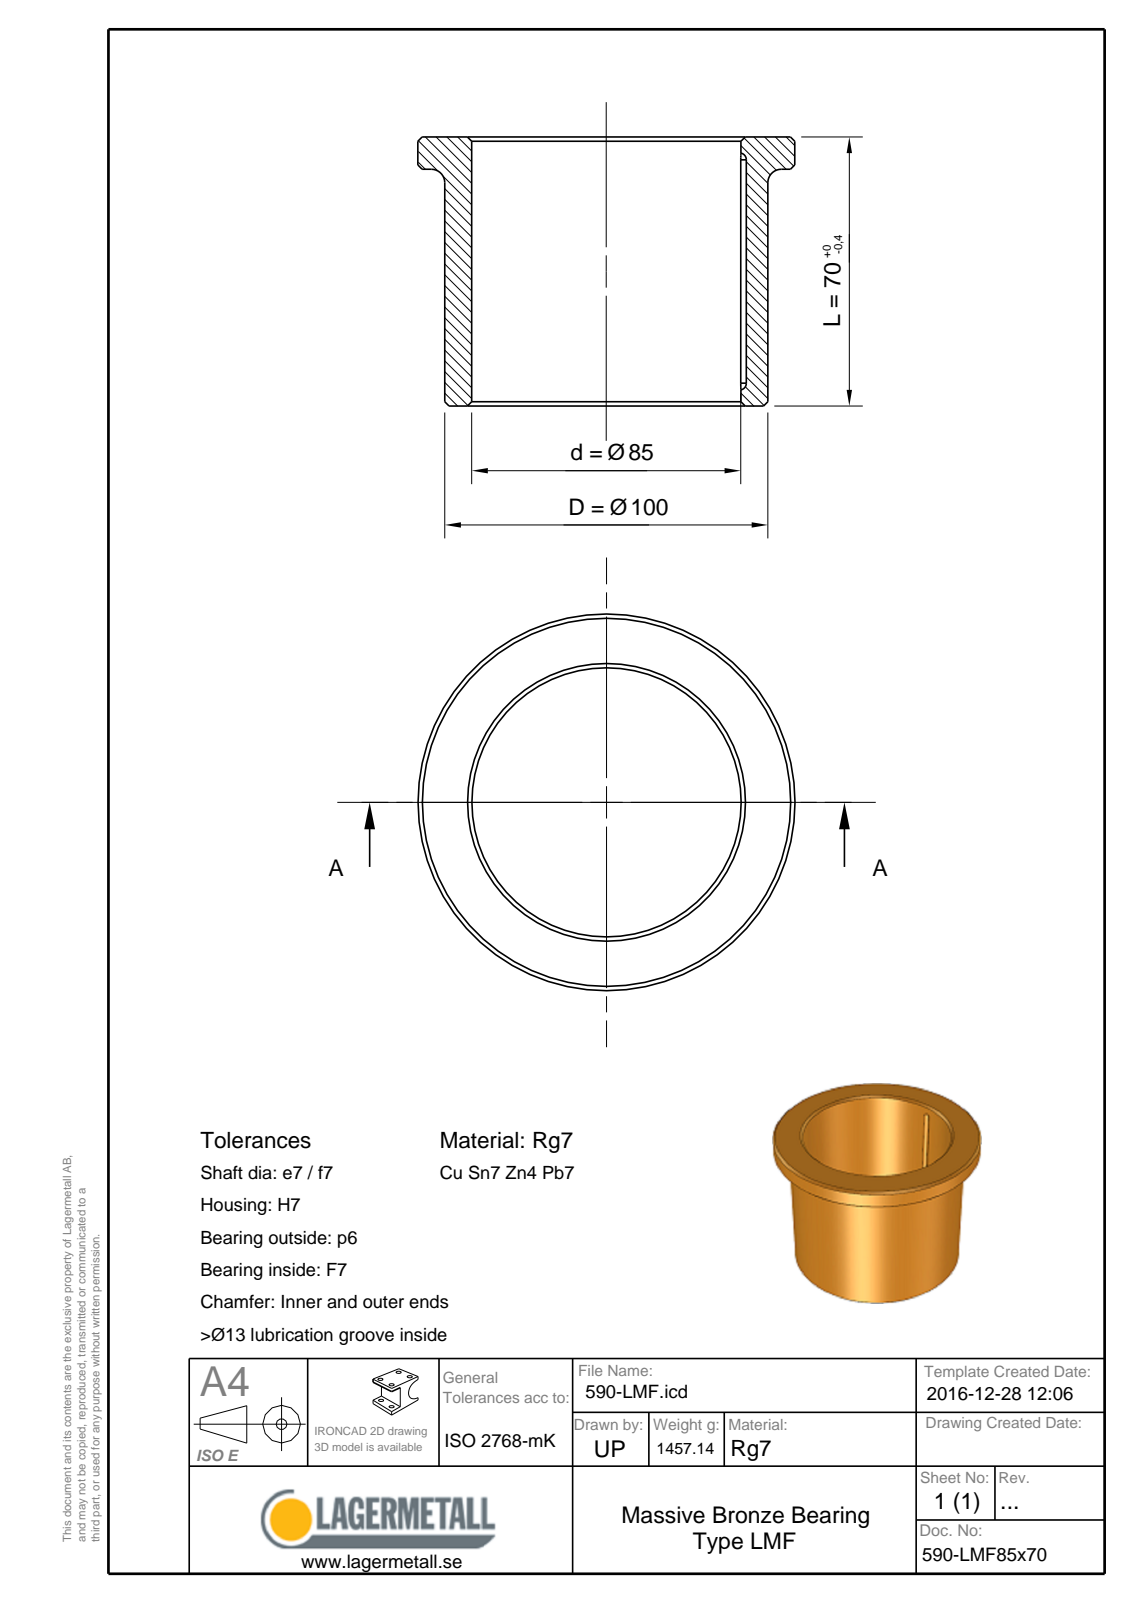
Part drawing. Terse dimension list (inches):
name: 590-LMF85x70
written by: Spatial InterOp 3D (CONFIG_CONTROL_DESIGN)
unit: in
bodies: 1 solid, 17 faces (4 planar, 5 cylindrical, 8 other)
size: 4.331 × 4.331 × 2.756
volume: 10.1 in³; area: 73.35 in²
holes: 1× ⌀3.346
bosses: 1× ⌀4.331, 1× ⌀3.937
rounds: 2× R0.069
face distances: 2.756, 2.441, 0.315
